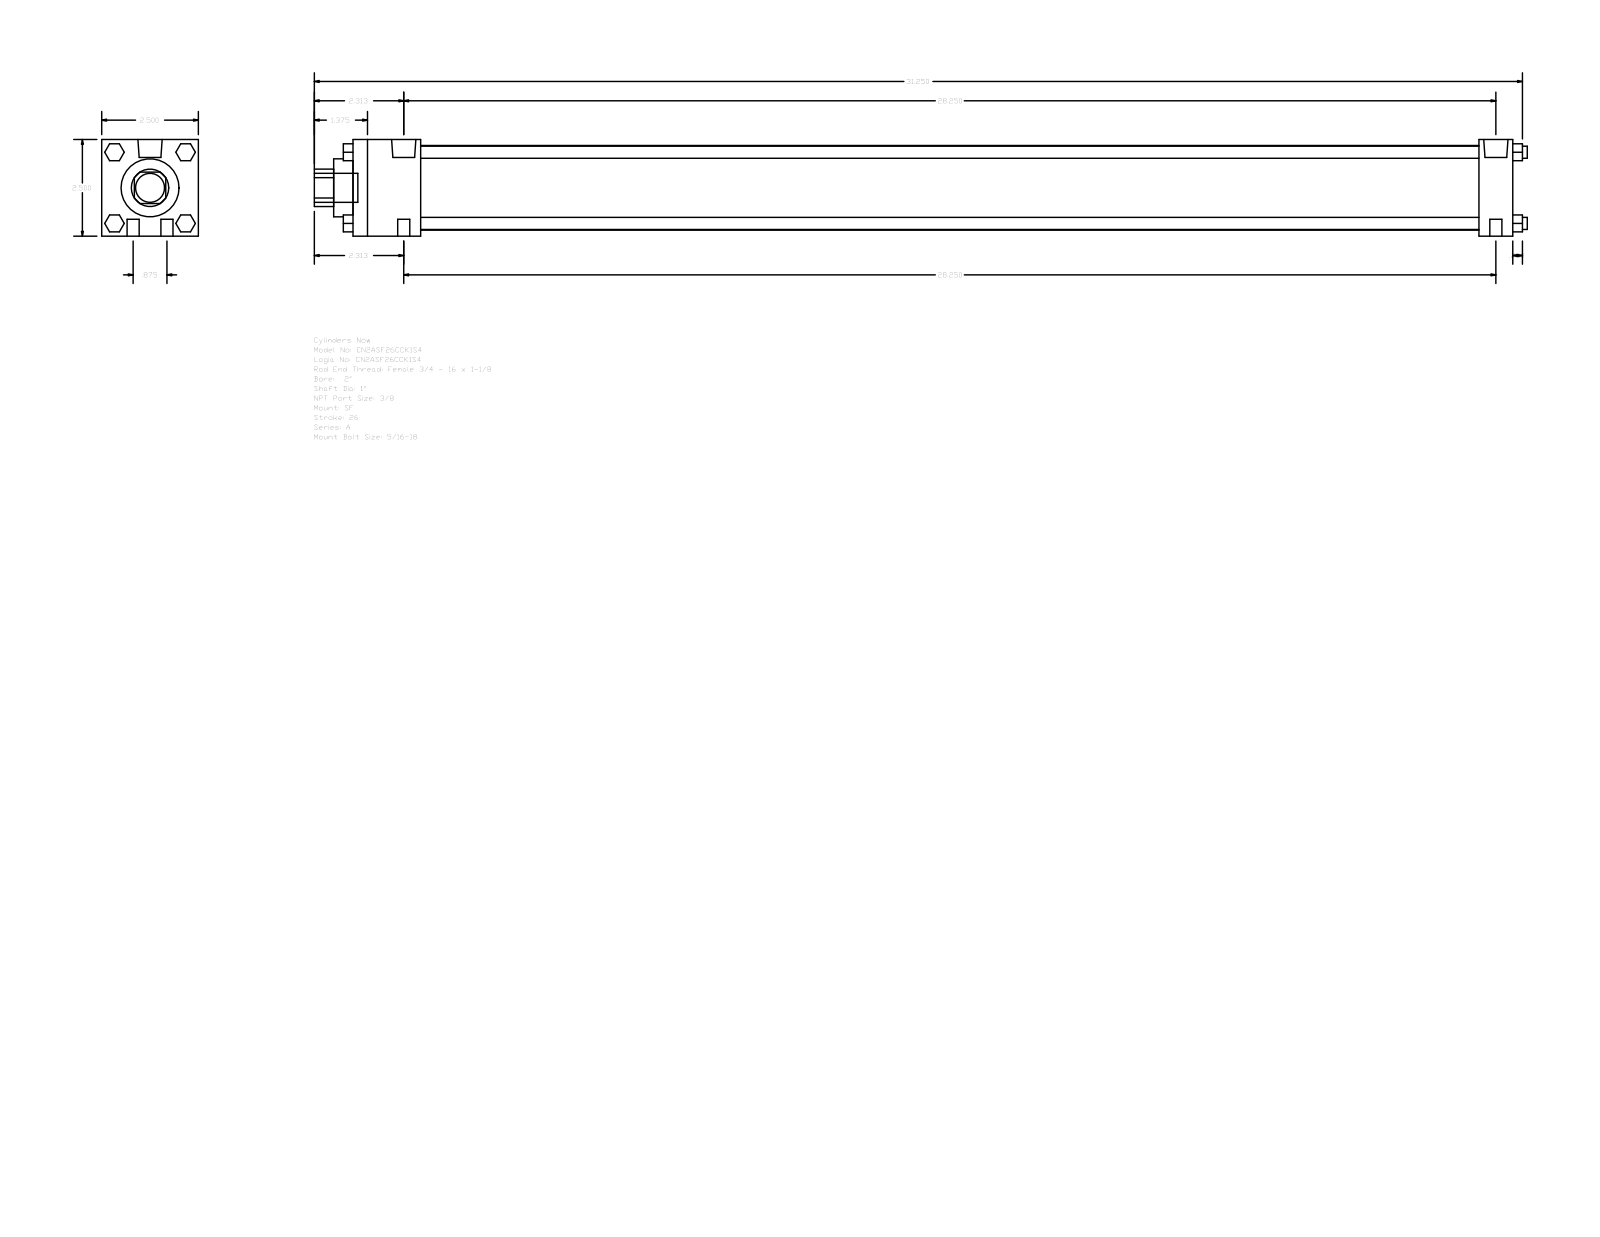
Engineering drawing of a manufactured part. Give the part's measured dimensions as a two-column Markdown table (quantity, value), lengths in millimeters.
| quantity | value |
| --- | --- |
| part name | A_SF__0200_1 |
| STEP written by | GSSL Pune (CONFIG_CONTROL_DESIGN) |
| units | millimeters |
| bodies | 0 solids, 124 faces (94 planar, 30 cylindrical, 0 other) |
| overall size | 796.92 × 63.5 × 63.5 |
| round holes (diameter × count) | 25.4 × 1, 38.1 × 1, 55.63 × 1 |
| round bosses / shafts (diameter × count) | 7.94 × 8, 15.93 × 2, 5.56 × 2, 19.05 × 1 |
| partial cylindrical surfaces (radius × count) | 12.29 × 1 |
| main face-to-face distances | 63.5, 762, 739.77, 22.23, 44.45, 695.32, 717.55, 12.7, 774.7, 6.35 |
